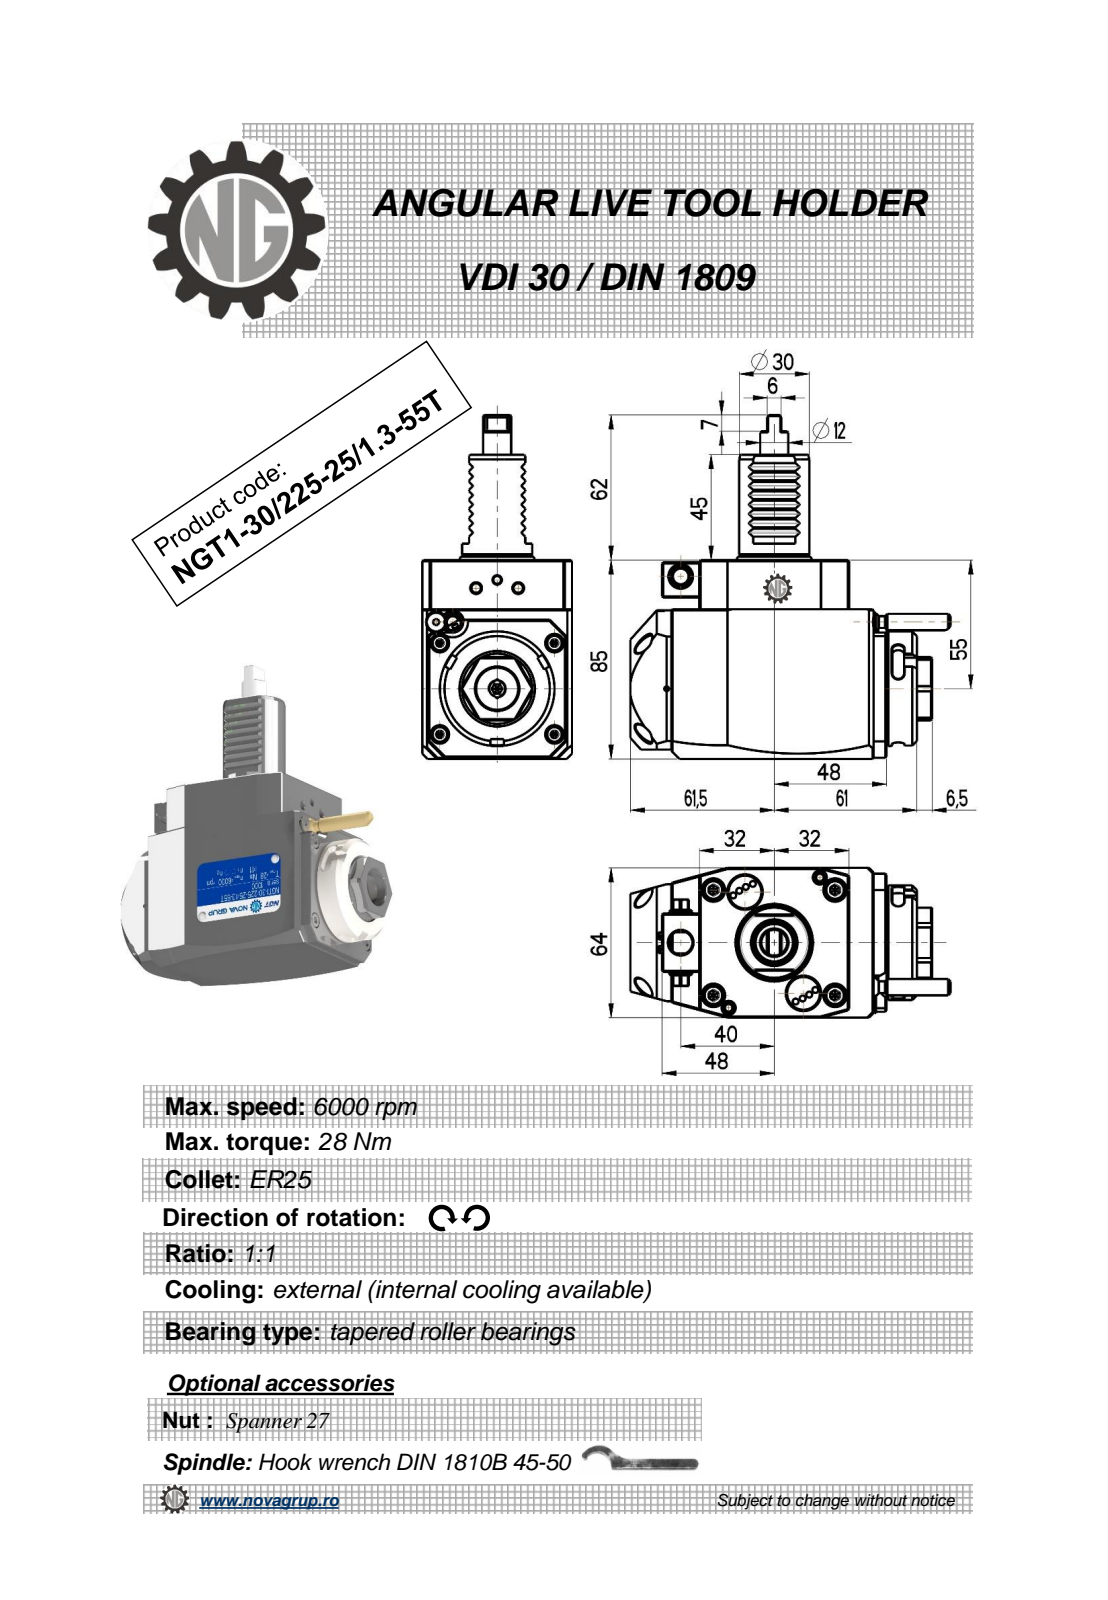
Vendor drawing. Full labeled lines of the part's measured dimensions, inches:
Part name (STEP PRODUCT): NGT1_30_225_25_1_3_55T
STEP written by: PRO/ENGINEER BY PARAMETRIC TECHNOLOGY CORPORATION, 2010280 (CONFIG_CONTROL_DESIGN)
Units: inches
Bodies: 1 solid, 378 faces (212 planar, 92 cylindrical, 74 other)
Overall size (bounding box): 5.787 × 5.389 × 2.52
Volume: 33.34 in³ · Surface area: 76.32 in²
Round holes (diameter × count): ⌀0.098 ×1, ⌀0.118 ×1, ⌀0.374 ×1, ⌀0.394 ×1, ⌀0.709 ×1
Round bosses / shafts (diameter × count): ⌀0.315 ×2, ⌀1.929 ×1, ⌀1.654 ×1, ⌀1.181 ×1, ⌀0.472 ×1, ⌀0.394 ×1, ⌀0.276 ×1, ⌀0.197 ×1
Partial cylindrical surfaces — rounded edges, fillets, slot ends (radius × count): R0.012 ×16, R0.098 ×6, R0.031 ×2, R7.087 ×2, R0.152 ×1, R0.167 ×1, R0.177 ×1, R0.591 ×1
Main face-to-face distances: 2.52, 3.346, 0.63, 3.15, 0.512, 4.311, 0.827, 1.142, 4.823, 3.681
Hole centre spacings: 1.03, 1.348, 1.831
